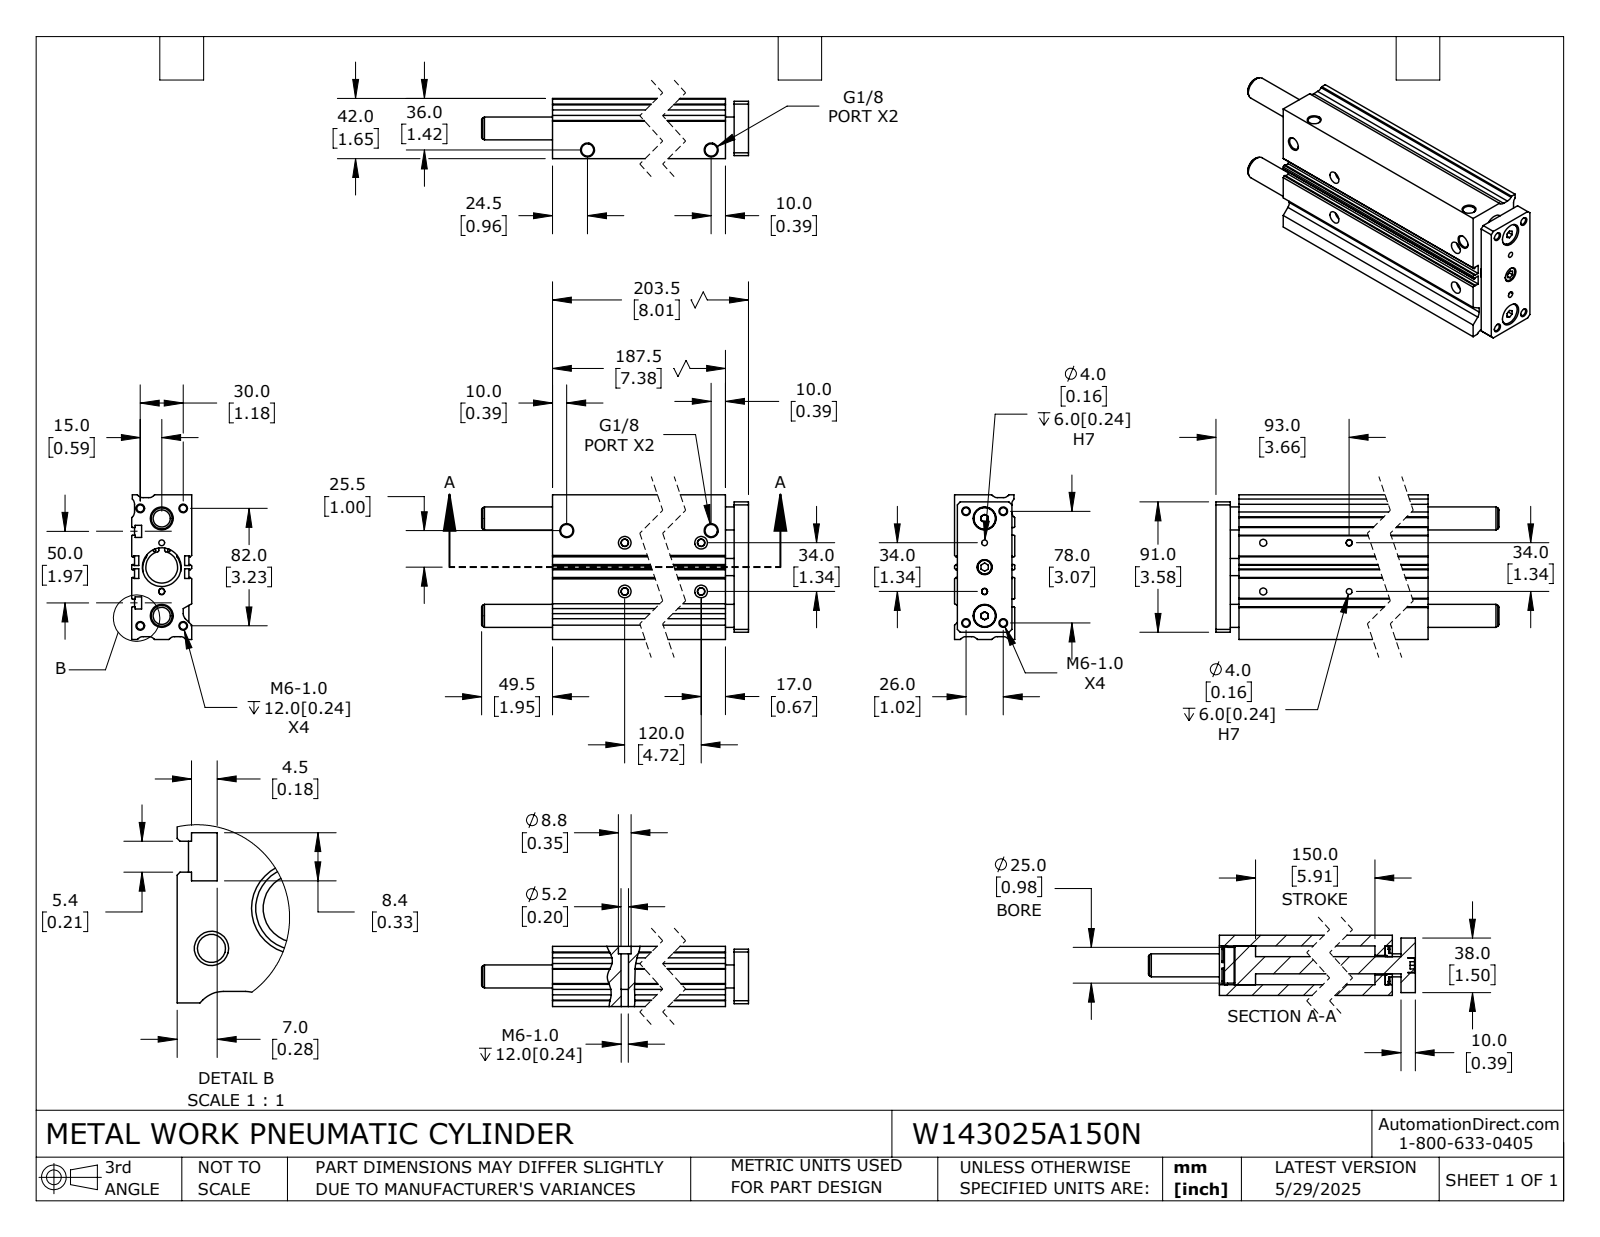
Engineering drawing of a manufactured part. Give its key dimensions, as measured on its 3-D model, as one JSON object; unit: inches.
{"part_name": "W143025A150N_BODY; W143025A150N_ROD; W143025A150N", "step_written_by": "SolidWorks 2024 (CONFIG_CONTROL_DESIGN)", "units": "inches", "bodies": {"solids": 6, "faces": 390, "planar": 191, "cylindrical": 157, "other": 42}, "overall_size": [9.961, 3.976, 1.654], "volume_in3": 42.84, "surface_area_in2": 257.4, "round_holes": [[0.194, 8], [0.067, 4], [0.157, 4], [0.194, 4], [0.205, 4], [0.337, 4], [0.346, 4], [0.63, 2], [0.413, 1], [0.472, 1], [0.539, 1], [0.874, 1]], "round_bosses_or_shafts": [[0.61, 2], [1.063, 1], [0.984, 1], [0.65, 1], [0.394, 1]], "partial_cylinders_radius": [[0.039, 12], [0.197, 9], [0.079, 8], [0.524, 2], [0.559, 1]], "face_to_face_distances": [1.654, 0.197, 0.079, 1.378, 1.457, 0.118, 0.236, 0.839, 3.976, 2.299], "hole_center_spacings": [1.339, 0.111, 0.29, 0.5, 0.548, 0.652, 0.669, 0.902]}
